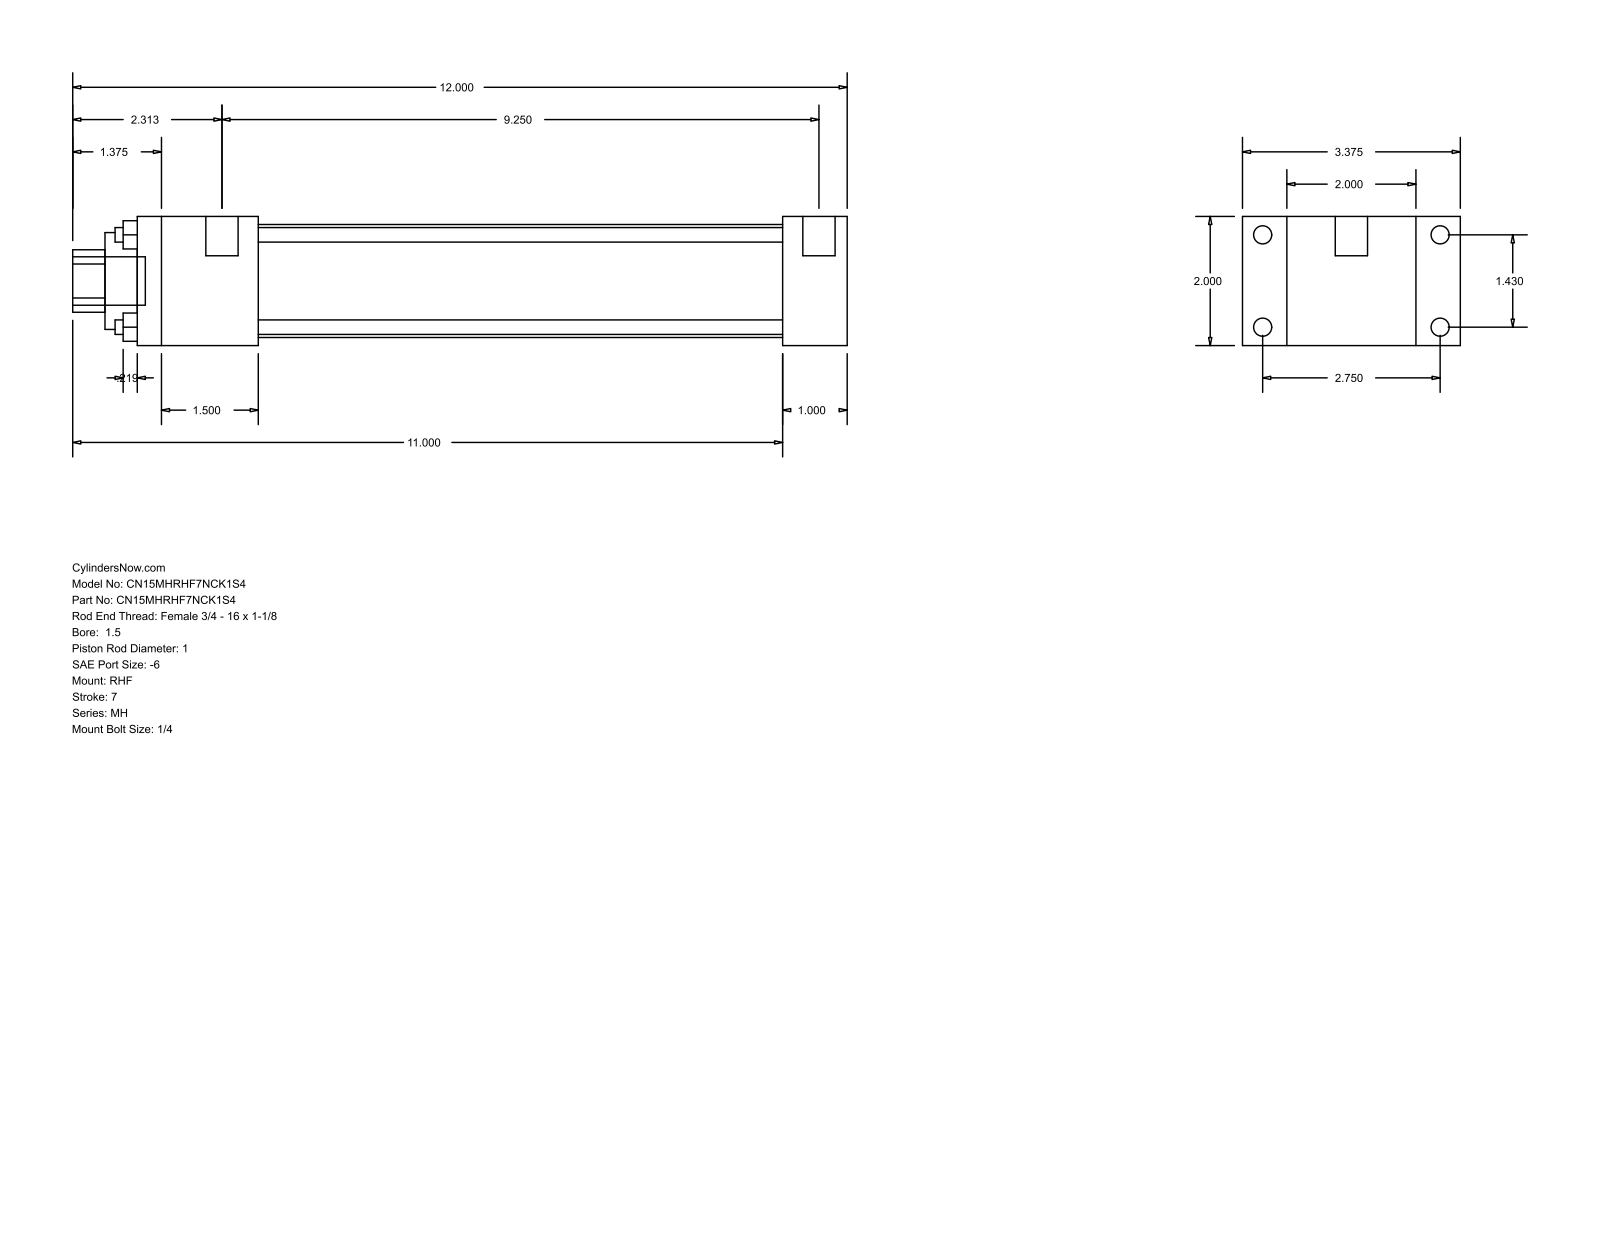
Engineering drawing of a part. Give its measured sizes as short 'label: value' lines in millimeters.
name: MH_RHF__0150_1
written by: GSSL Pune (CONFIG_CONTROL_DESIGN)
unit: mm
bodies: 0 solids, 88 faces (60 planar, 28 cylindrical, 0 other)
size: 304.8 × 85.72 × 50.8
holes: 4× ⌀5.71, 1× ⌀25.4, 1× ⌀38.1, 1× ⌀44.45
bosses: 4× ⌀7.14, 4× ⌀5.56, 2× ⌀12.7, 1× ⌀19.05
rounds: 1× R12.29
face distances: 50.8, 25.4, 17.46, 68.26, 85.72, 279.4, 254, 47.63, 206.37, 231.77
hole spacings: 25.68, 36.32, 51.36
